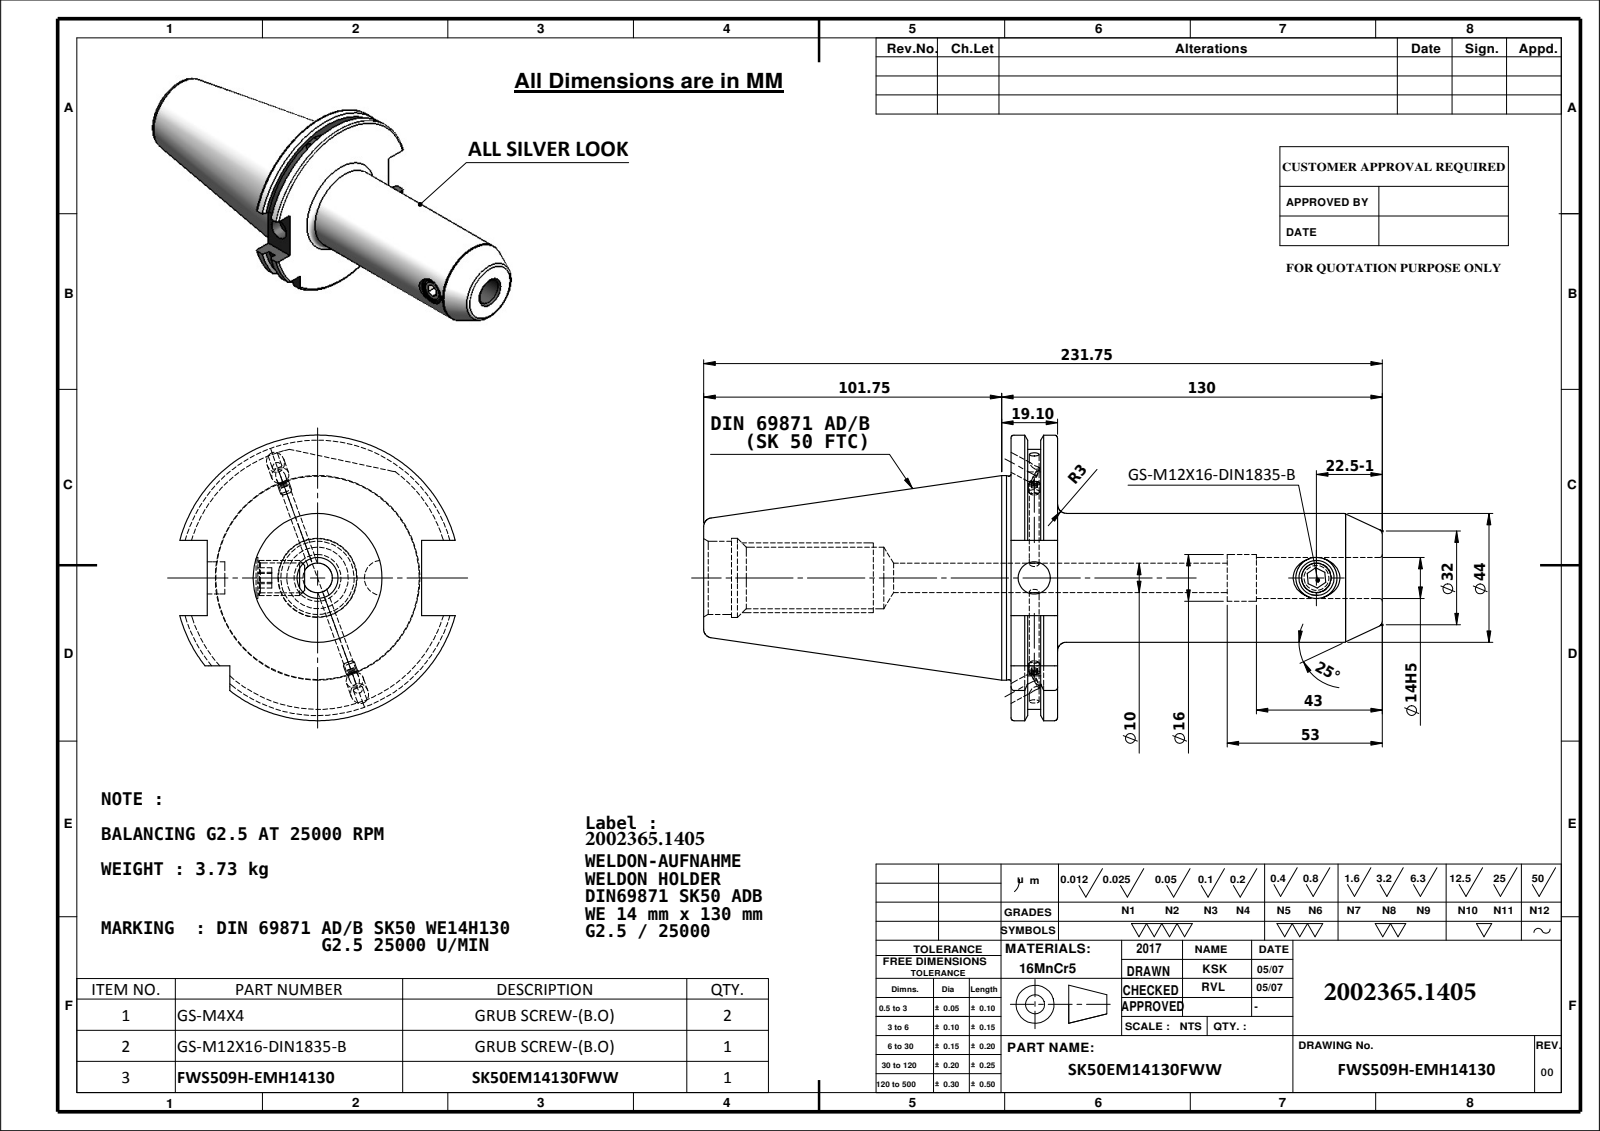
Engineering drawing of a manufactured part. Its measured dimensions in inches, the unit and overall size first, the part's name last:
Units: inches
Overall size (bounding box): 9.124 × 3.839 × 3.703
Round holes (diameter × count): ⌀0.236 ×2, ⌀0.551 ×2, ⌀0.13 ×1, ⌀0.394 ×1, ⌀0.402 ×1, ⌀0.433 ×1, ⌀0.63 ×1, ⌀0.827 ×1, ⌀0.984 ×1, ⌀1.063 ×1
Round bosses / shafts (diameter × count): ⌀0.157 ×2, ⌀2.75 ×1, ⌀2.734 ×1, ⌀1.732 ×1, ⌀0.472 ×1
Partial cylindrical surfaces — rounded edges, fillets, slot ends (radius × count): R1.768 ×1, R1.919 ×1
Main face-to-face distances: 0.626, 0.4, 0.226, 0.223, 0.177, 0.403, 4.992, 4.769, 4.593, 4.366
Hole centre spacings: 3.795
Volume: 29.53 in³ · Surface area: 98.3 in²
Bodies: 4 solids, 168 faces (53 planar, 55 cylindrical, 60 other)
Part name (STEP PRODUCT): SK50EM14130FWW; Copy of M4X4_DIN 913 - M4 x 4-N; 91506-WE714130; M12X16_ISO 4026 - M12 x 12-N
STEP written by: SolidWorks 2009 (CONFIG_CONTROL_DESIGN)
